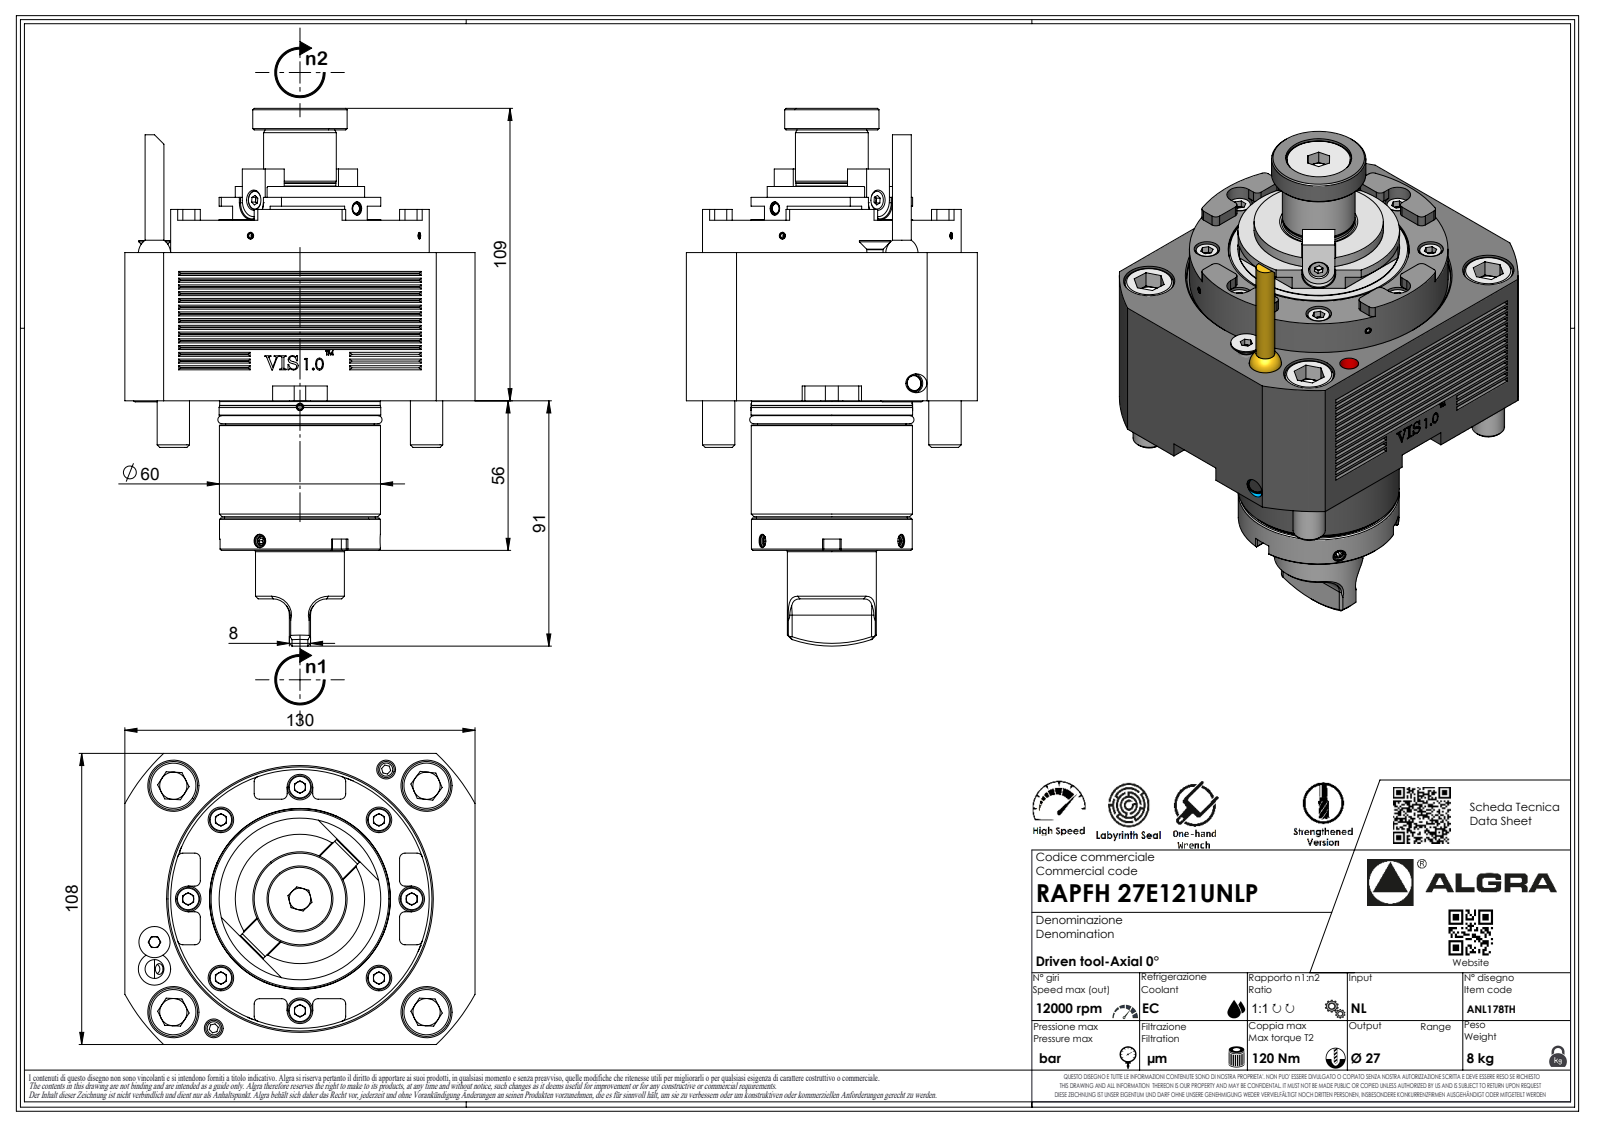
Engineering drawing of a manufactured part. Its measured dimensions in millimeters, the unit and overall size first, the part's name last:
Units: millimetres
Overall size (bounding box): 199.5 × 130 × 108
Round holes (diameter × count): ⌀2.1 ×1
Round bosses / shafts (diameter × count): ⌀12 ×4, ⌀96 ×1, ⌀60 ×1, ⌀48 ×1, ⌀35 ×1, ⌀33 ×1, ⌀27 ×1, ⌀6.37 ×1
Partial cylindrical surfaces — rounded edges, fillets, slot ends (radius × count): R2 ×24, R6 ×10, R8 ×8, R0.33 ×7, R0.52 ×7, R3.7 ×7, R4.75 ×4, R0.21 ×1
Main face-to-face distances: 55, 108, 12, 130, 67, 55.5, 110.5, 122.5, 4, 8.5
Volume: 1 061 000 mm³ · Surface area: 80 844 mm²
Bodies: 1 solid, 509 faces (348 planar, 90 cylindrical, 71 other)
Part name (STEP PRODUCT): RAPFH27E121UNLP
STEP written by: SolidWorks 2023 (AUTOMOTIVE_DESIGN)
